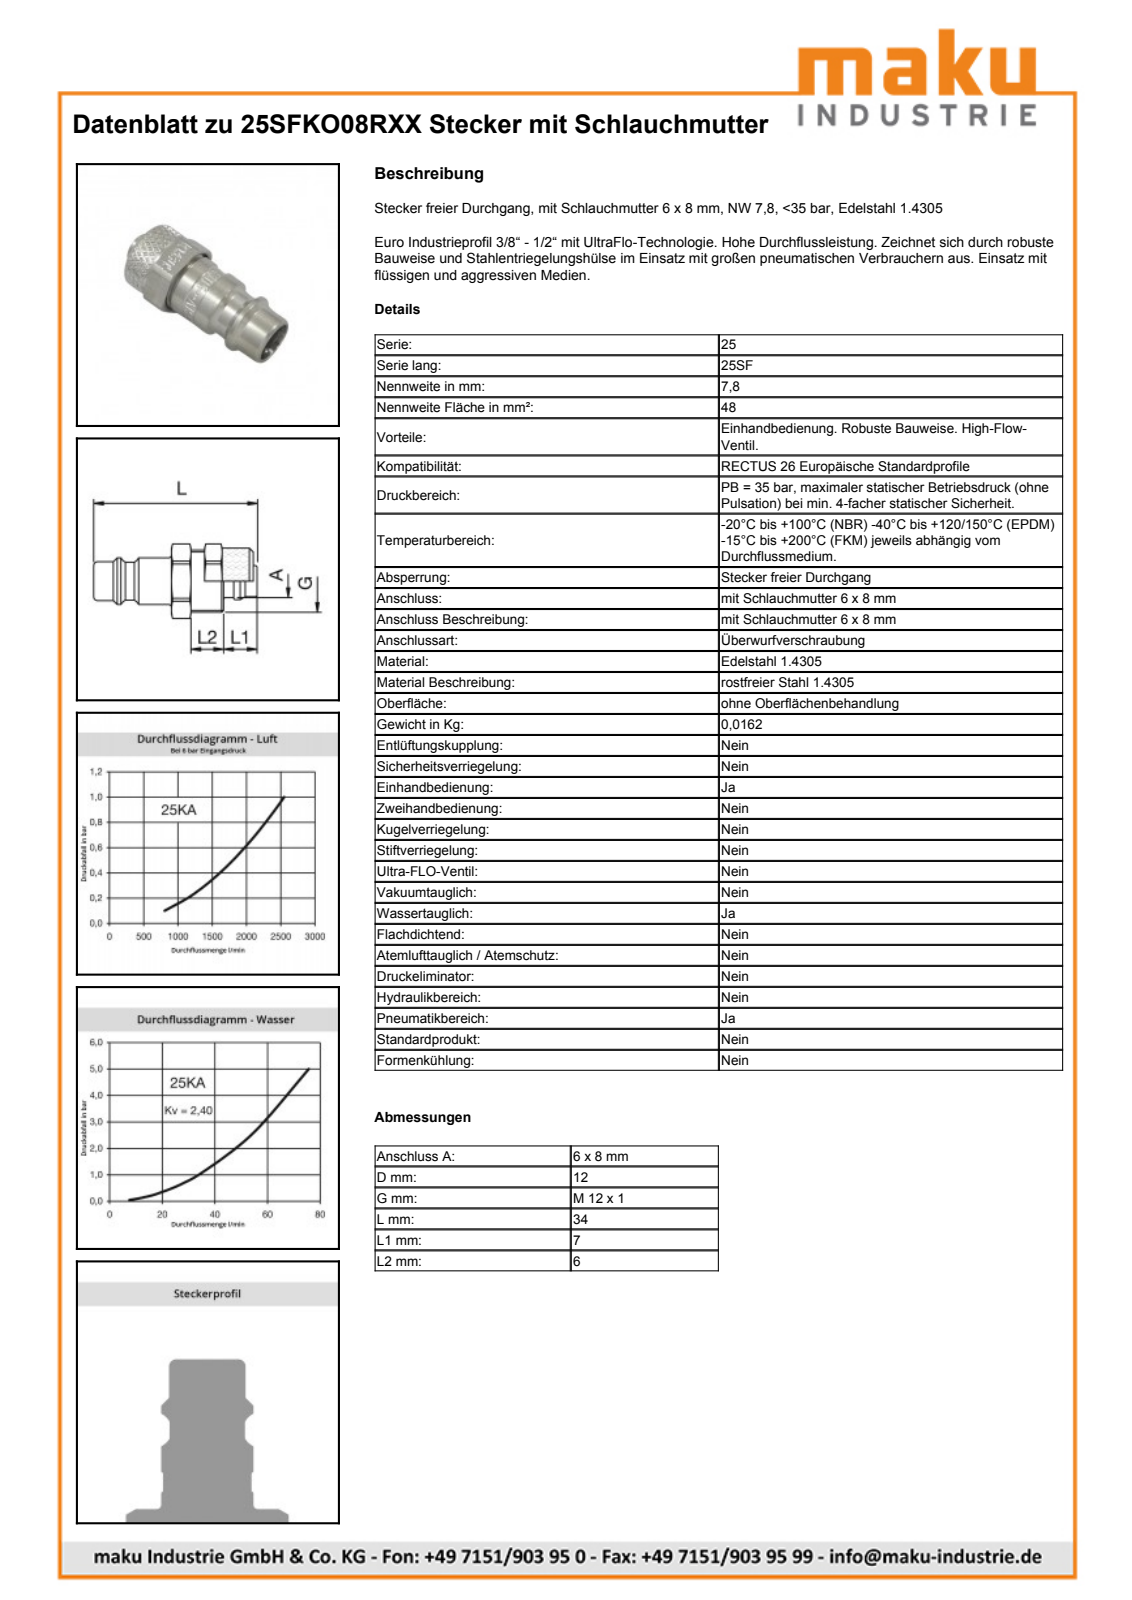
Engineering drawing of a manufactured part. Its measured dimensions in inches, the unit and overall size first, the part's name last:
Units: inches
Overall size (bounding box): 1.339 × 0.61 × 0.567
Round holes (diameter × count): ⌀0.193 ×1, ⌀0.309 ×1, ⌀0.325 ×1, ⌀0.492 ×1
Round bosses / shafts (diameter × count): ⌀0.551 ×1, ⌀0.472 ×1, ⌀0.39 ×1, ⌀0.384 ×1, ⌀0.264 ×1, ⌀0.238 ×1
Partial cylindrical surfaces — rounded edges, fillets, slot ends (radius × count): R0.305 ×1
Main face-to-face distances: 0.551, 0.243, 0.433, 0.19, 0.032, 0.276, 0.465, 1.339, 1.306, 1.063
Volume: 0.131 in³ · Surface area: 4.767 in²
Bodies: 2 solids, 56 faces (12 planar, 18 cylindrical, 26 other)
Part name (STEP PRODUCT): D113216; D113214; D105558
STEP written by: Autodesk Inventor 2013 (AUTOMOTIVE_DESIGN)
